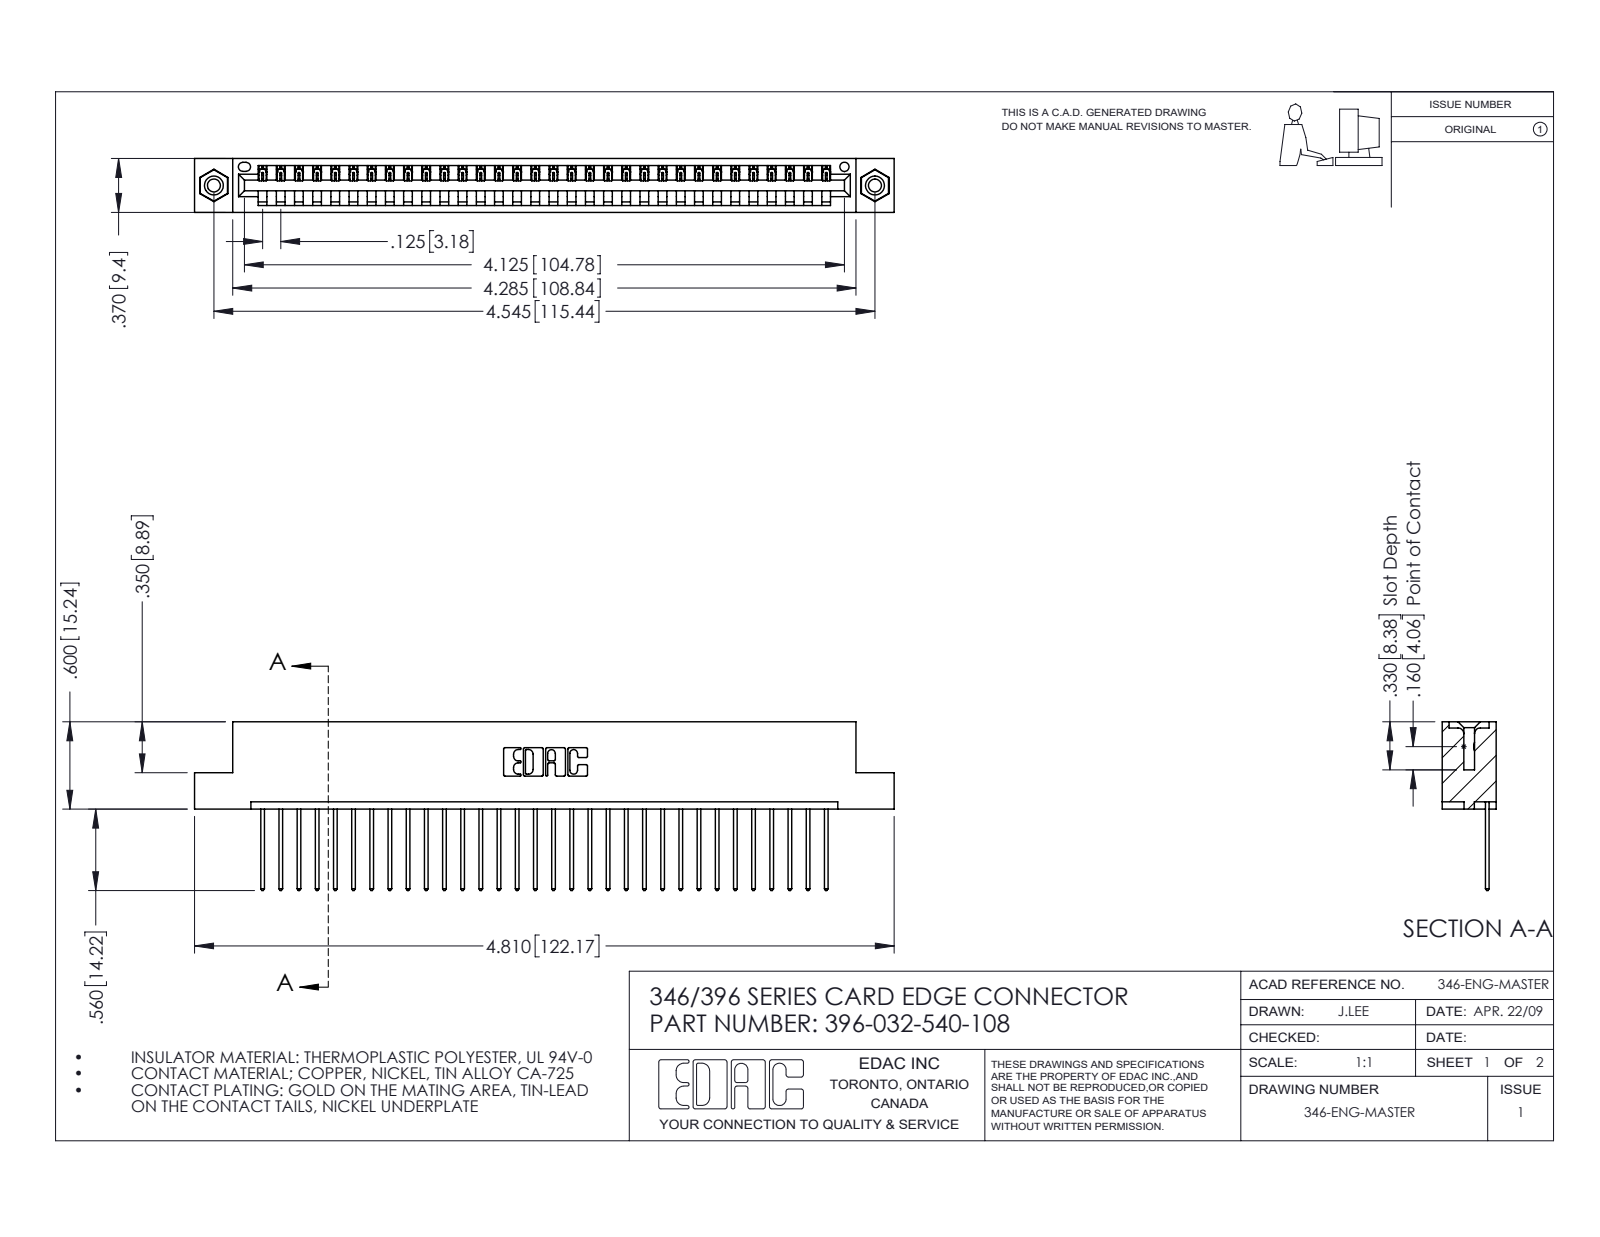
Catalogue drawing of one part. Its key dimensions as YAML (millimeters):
part_name: "396-032-540-108; 345-292-001_345-293-140; 345-250-001_345-250-003-102; 346 Part_Flush Mounting Lugs - 0.156 Dia-TI"
step_written_by: "SolidWorks 2016 (CONFIG_CONTROL_DESIGN)"
units: millimeters
bodies: {solids: 35, faces: 2038, planar: 1388, cylindrical: 634, other: 16}
overall_size: [122.2, 29.5, 9.4]
volume: 11700
surface_area: 14810
round_holes:
  - {diameter: 2.3, count: 2}
  - {diameter: 3.2, count: 2}
  - {diameter: 4, count: 2}
  - {diameter: 1.6, count: 1}
round_bosses_or_shafts:
  - {diameter: 3.9, count: 2}
partial_cylinders:
  - {radius: 0.2, count: 64}
  - {radius: 0.3, count: 64}
  - {radius: 0.3, count: 22}
  - {radius: 0.2, count: 6}
  - {radius: 0.8, count: 6}
  - {radius: 0.7, count: 3}
  - {radius: 0.8, count: 2}
  - {radius: 1, count: 2}
face_to_face_distances: [1.2, 8.2, 9.4, 6.4, 1.8, 7.6, 0.6, 3.8, 5.6, 2.5]
hole_center_spacings: [6.2, 110.2, 115.4]
